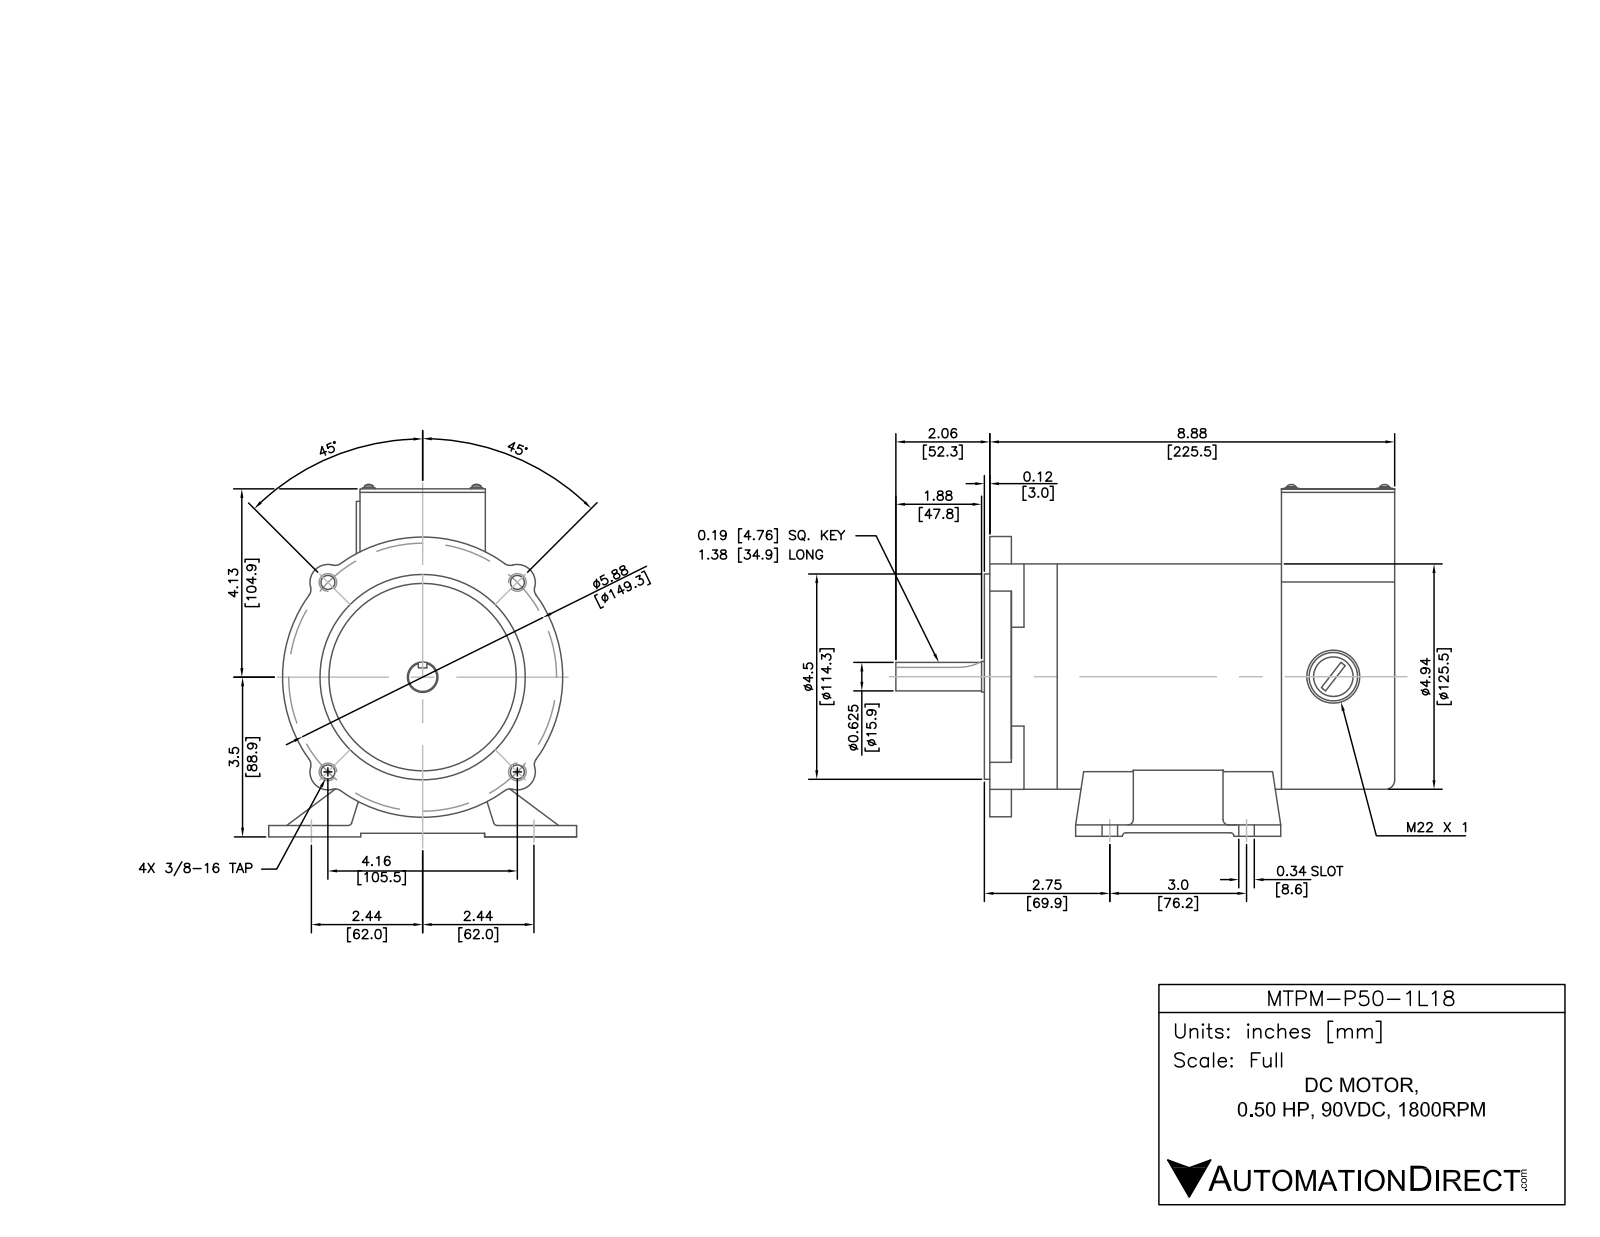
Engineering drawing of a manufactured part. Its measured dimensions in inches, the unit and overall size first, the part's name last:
Units: inches
Overall size (bounding box): 10.972 × 7.521 × 6.496
Round holes (diameter × count): ⌀0.197 ×8, ⌀0.13 ×6, ⌀0.098 ×2, ⌀0.169 ×2, ⌀0.205 ×2, ⌀0.236 ×2, ⌀0.276 ×2, ⌀0.299 ×2, ⌀0.374 ×2, ⌀0.394 ×2, ⌀0.728 ×2, ⌀1.575 ×2
Round bosses / shafts (diameter × count): ⌀0.157 ×6, ⌀0.354 ×4, ⌀0.331 ×4, ⌀1.929 ×2, ⌀0.39 ×2, ⌀6.142 ×1, ⌀4.937 ×1, ⌀4.74 ×1
Partial cylindrical surfaces — rounded edges, fillets, slot ends (radius × count): R0.197 ×38, R0.02 ×34, R0.039 ×28, R0.098 ×14, R0.236 ×10, R0.118 ×8, R0.157 ×8, R0.169 ×8
Main face-to-face distances: 0.098, 0.157, 0.079, 0.059, 8.894, 8.953, 8.795, 0.256, 0.276, 0.472
Hole centre spacings: 0.05, 1.187, 1.89, 2.166, 2.262, 2.362, 2.749, 0.104
Volume: 61.49 in³ · Surface area: 632.7 in²
Bodies: 28 solids, 1249 faces (366 planar, 571 cylindrical, 312 other)
Part name (STEP PRODUCT): WPMDC12-18-90-180-56CB
STEP written by: SolidWorks 2017 (AUTOMOTIVE_DESIGN)
